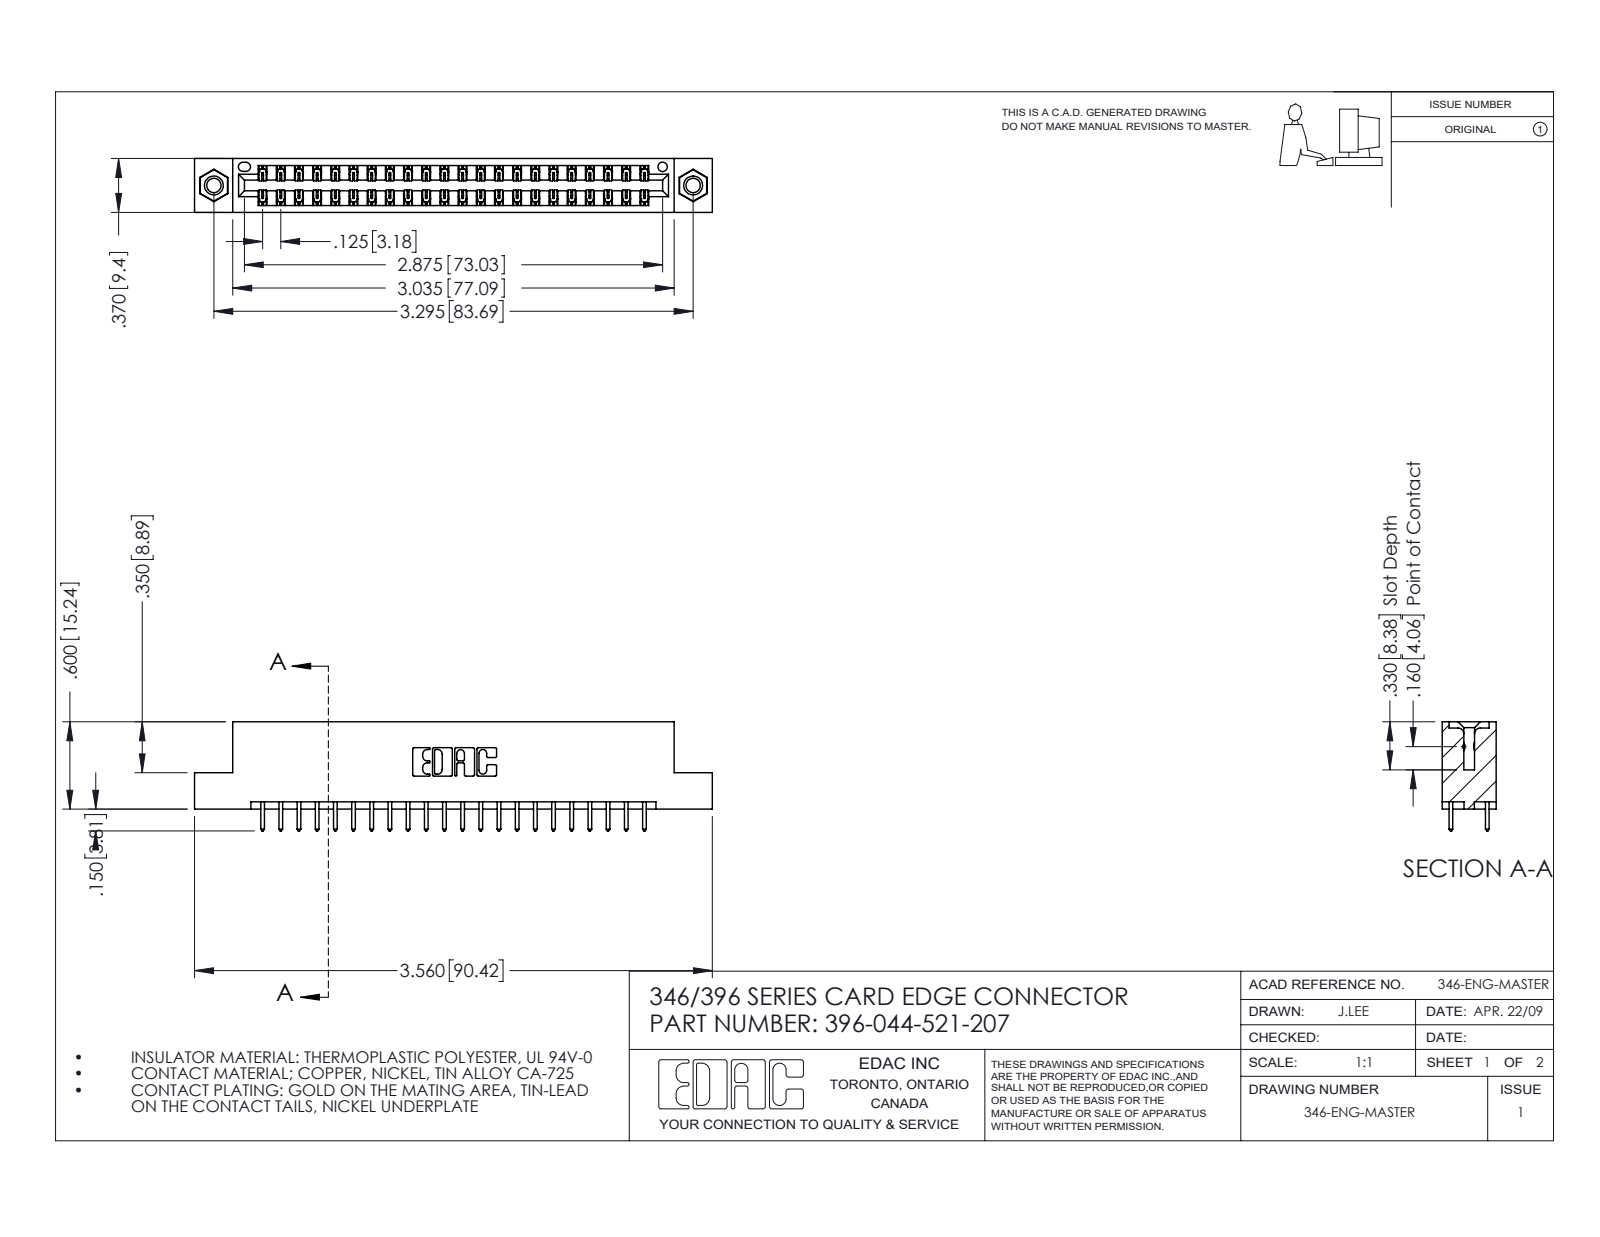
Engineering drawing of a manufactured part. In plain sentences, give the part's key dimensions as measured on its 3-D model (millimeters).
The part is named "345-250-001_345-250-005-103; 346 Part_Flush Mounting Lugs - 0.156 Dia-TI; 345-292-001_345-293-121; 396-044-521-207". Its 3-D file was written by "SolidWorks 2016 (CONFIG_CONTROL_DESIGN)". It is 47 solids with 2470 faces: 1648 planar, 806 cylindrical and 16 other. Overall it measures 90.4 by 19.1 by 9.4 millimeters. Its volume is 8 640 cubic millimeters and its surface area 11 460 square millimeters. Round holes: 2 of diameter 2.5, 2 of diameter 3.2, 2 of diameter 4, 1 of diameter 1.6. Round bosses or shafts: 2 of diameter 3.9. Partial cylindrical surfaces (rounded edges, fillets, slot ends): 66 of radius 0.2, 44 of radius 0.3, 22 of radius 0.3, 6 of radius 0.2, 6 of radius 0.8, 3 of radius 0.7, 2 of radius 0.4, 2 of radius 0.6. The main face-to-face distances are 1.2, 8.2, 6.4, 9.4, 1.8, 7.6, 0.6, 7, 3.8, 5.6. The hole center spacings are 6.2, 78.4, 83.7.
